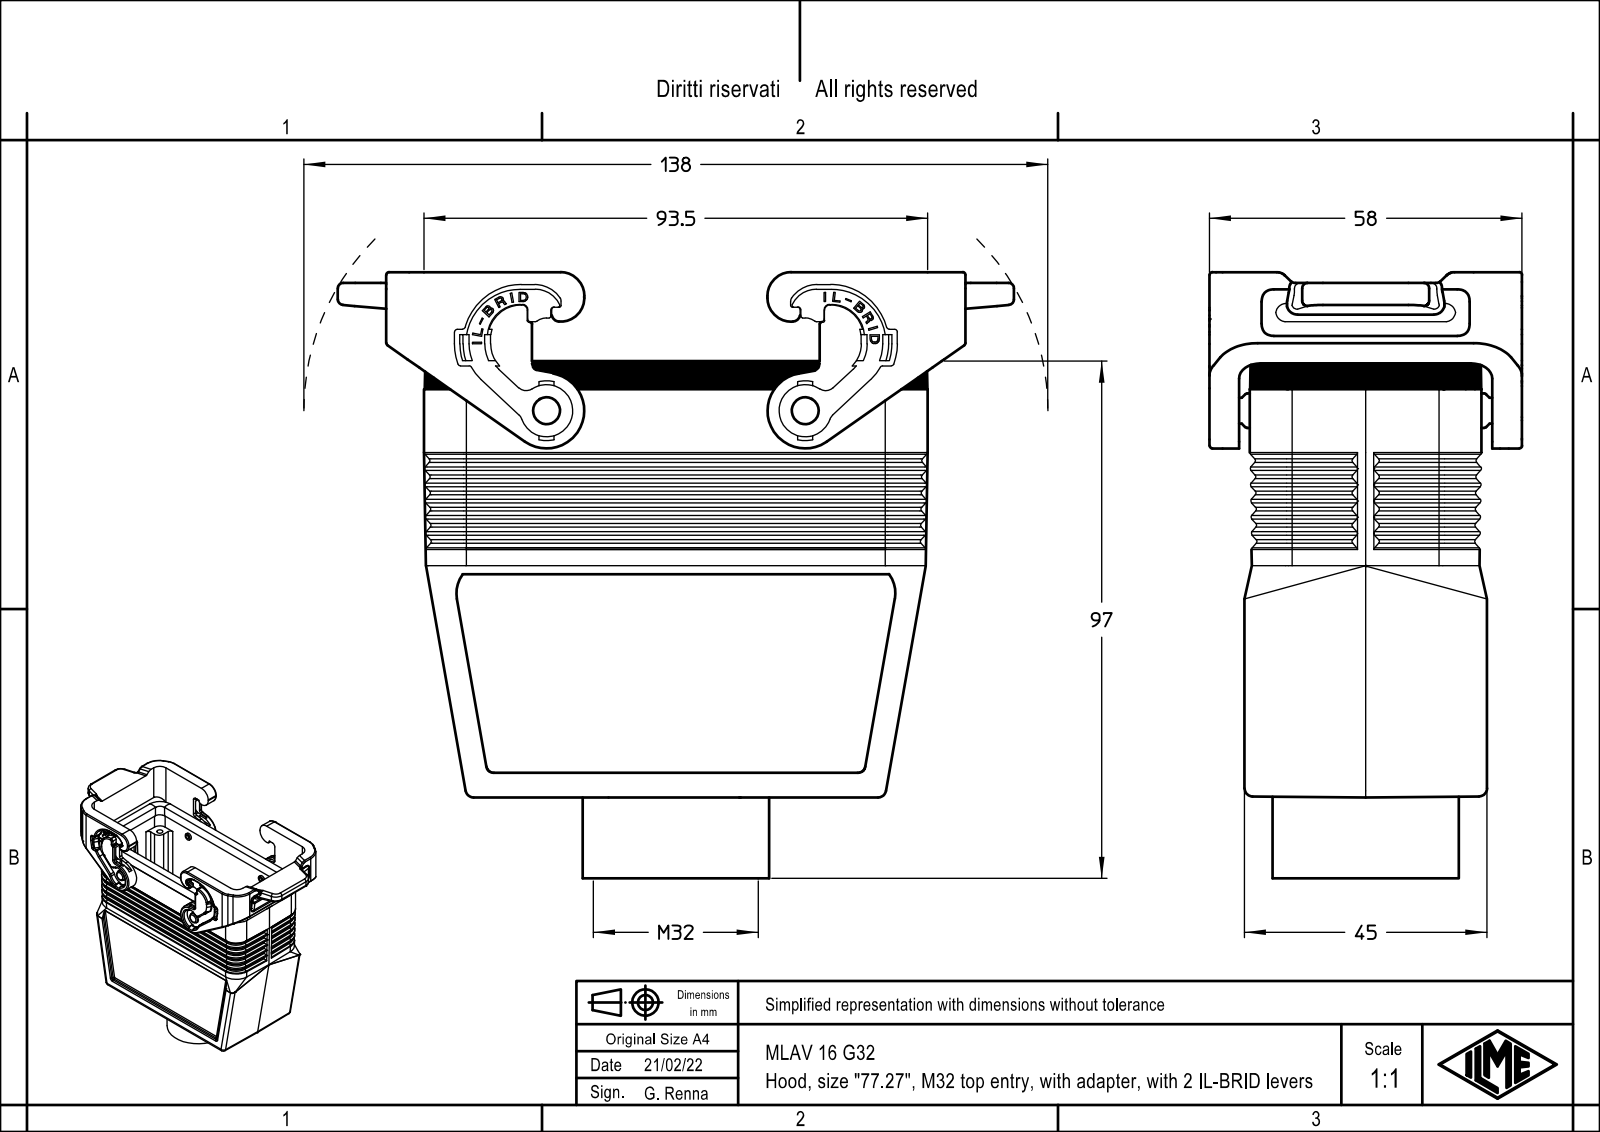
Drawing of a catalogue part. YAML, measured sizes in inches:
part_name: "MLAV_16_G32"
step_written_by: "Creo Elements/Direct Modeling 20.1B 02-Apr-2019 (C) Parametric Technology GmbH (AUTOMOTIVE_DESIGN)"
units: inches
bodies: {solids: 1, faces: 1613, planar: 1031, cylindrical: 397, other: 185}
overall_size: [4.941, 4.467, 2.283]
volume: 7.573
surface_area: 100.5
round_holes:
  - {diameter: 0.108, count: 4}
  - {diameter: 1.063, count: 1}
  - {diameter: 1.26, count: 1}
round_bosses_or_shafts:
  - {diameter: 0.268, count: 2}
  - {diameter: 0.189, count: 2}
  - {diameter: 1.417, count: 1}
partial_cylinders:
  - {radius: 0.02, count: 104}
  - {radius: 0.039, count: 46}
  - {radius: 0.118, count: 20}
  - {radius: 0.276, count: 16}
  - {radius: 0.013, count: 15}
  - {radius: 0.059, count: 14}
  - {radius: 0.012, count: 8}
  - {radius: 0.079, count: 8}
face_to_face_distances: [1.545, 0.148, 0.079, 0.039, 0.226, 0.187, 1.693, 1.772, 1.358, 1.506]
hole_center_spacings: [1.615, 1.063, 3.051, 3.231]
